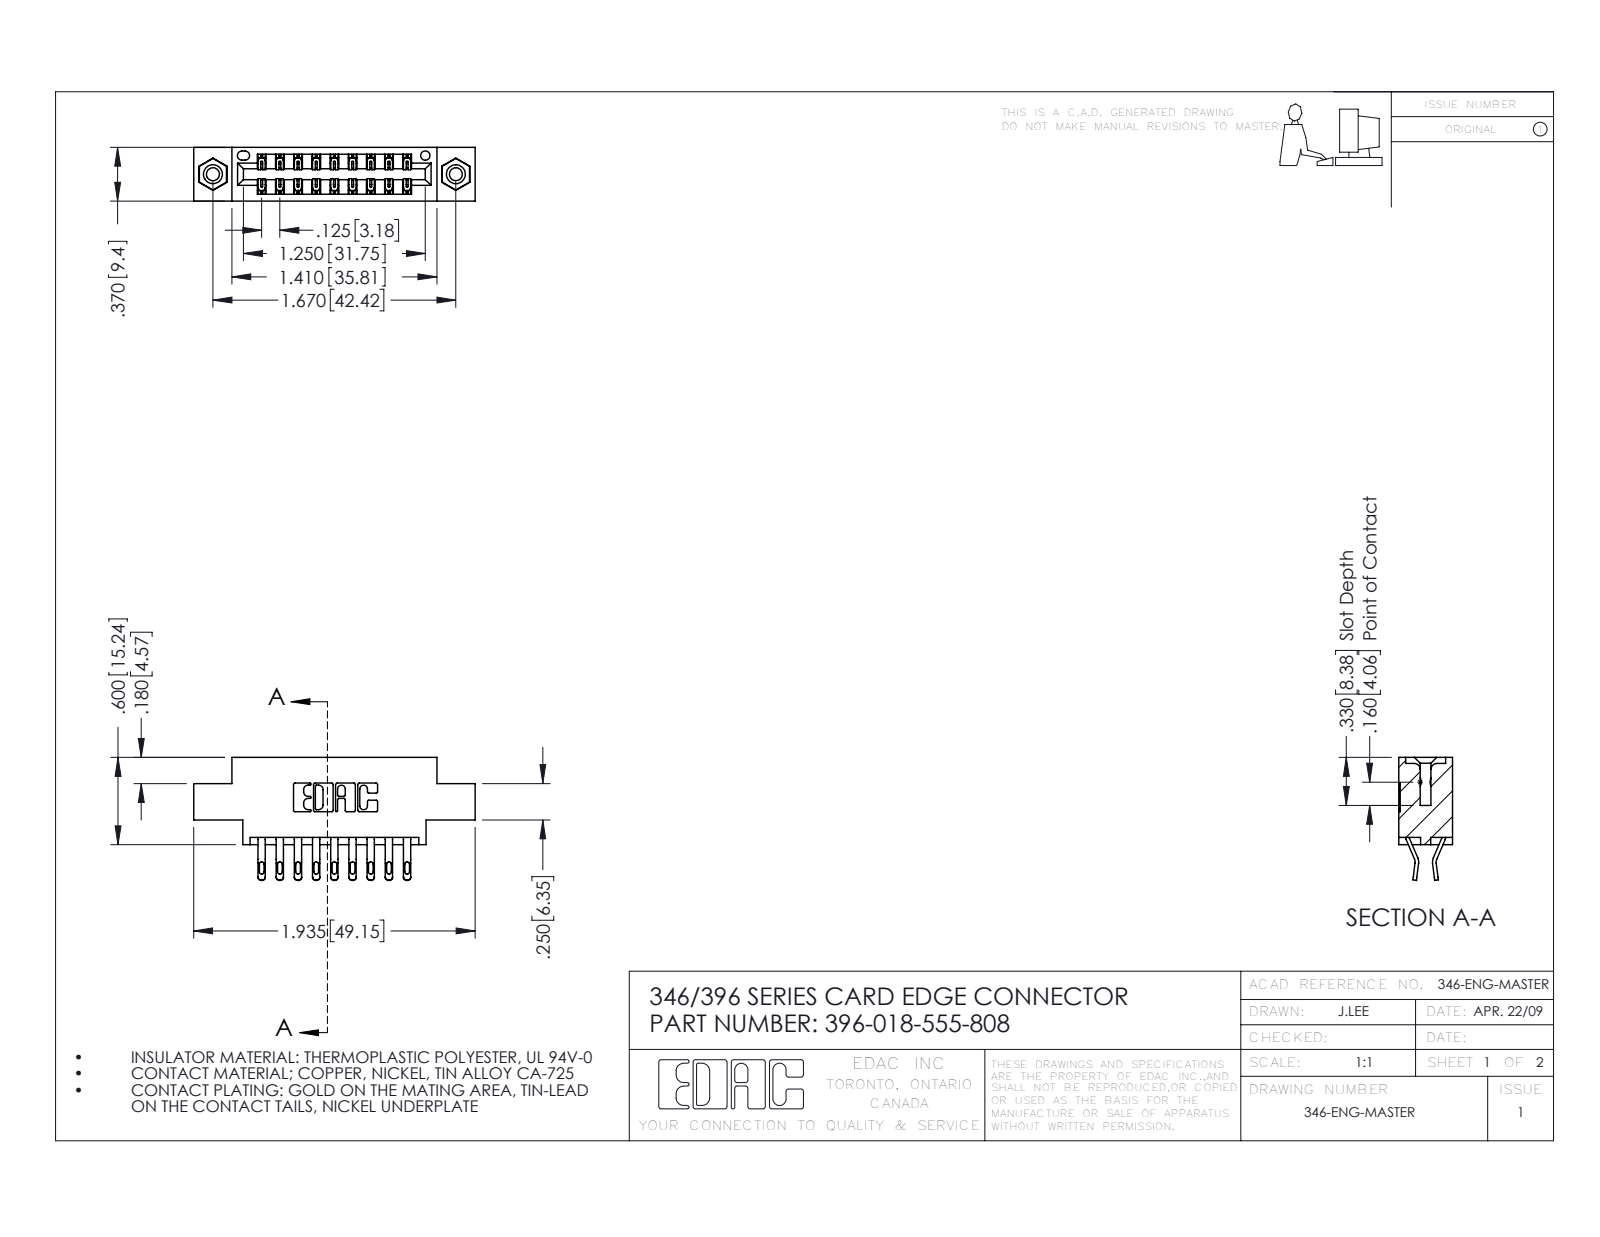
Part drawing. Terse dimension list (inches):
name: 396-018-555-808; 345-250-001_345-250-003-102; 345-292-001_555 Tail; 346 Part_0.170 Offset - 0.156 Dia-TI
written by: SolidWorks 2016 (CONFIG_CONTROL_DESIGN)
unit: in
bodies: 21 solids, 1230 faces (706 planar, 508 cylindrical, 16 other)
size: 1.935 × 0.845 × 0.37
volume: 0.27 in³; area: 9.227 in²
holes: 2× ⌀0.089, 2× ⌀0.125, 2× ⌀0.156, 1× ⌀0.064
bosses: 2× ⌀0.155
rounds: 36× R0.016, 36× R0.02, 27× R0.006, 22× R0.01, 6× R0.007, 6× R0.031, 3× R0.026, 2× R0.01
face distances: 0.25, 0.37, 0.048, 0.322, 0.222, 0.148, 0.025, 0.072, 0.298, 0.1
hole spacings: 0.246, 1.465, 1.67
